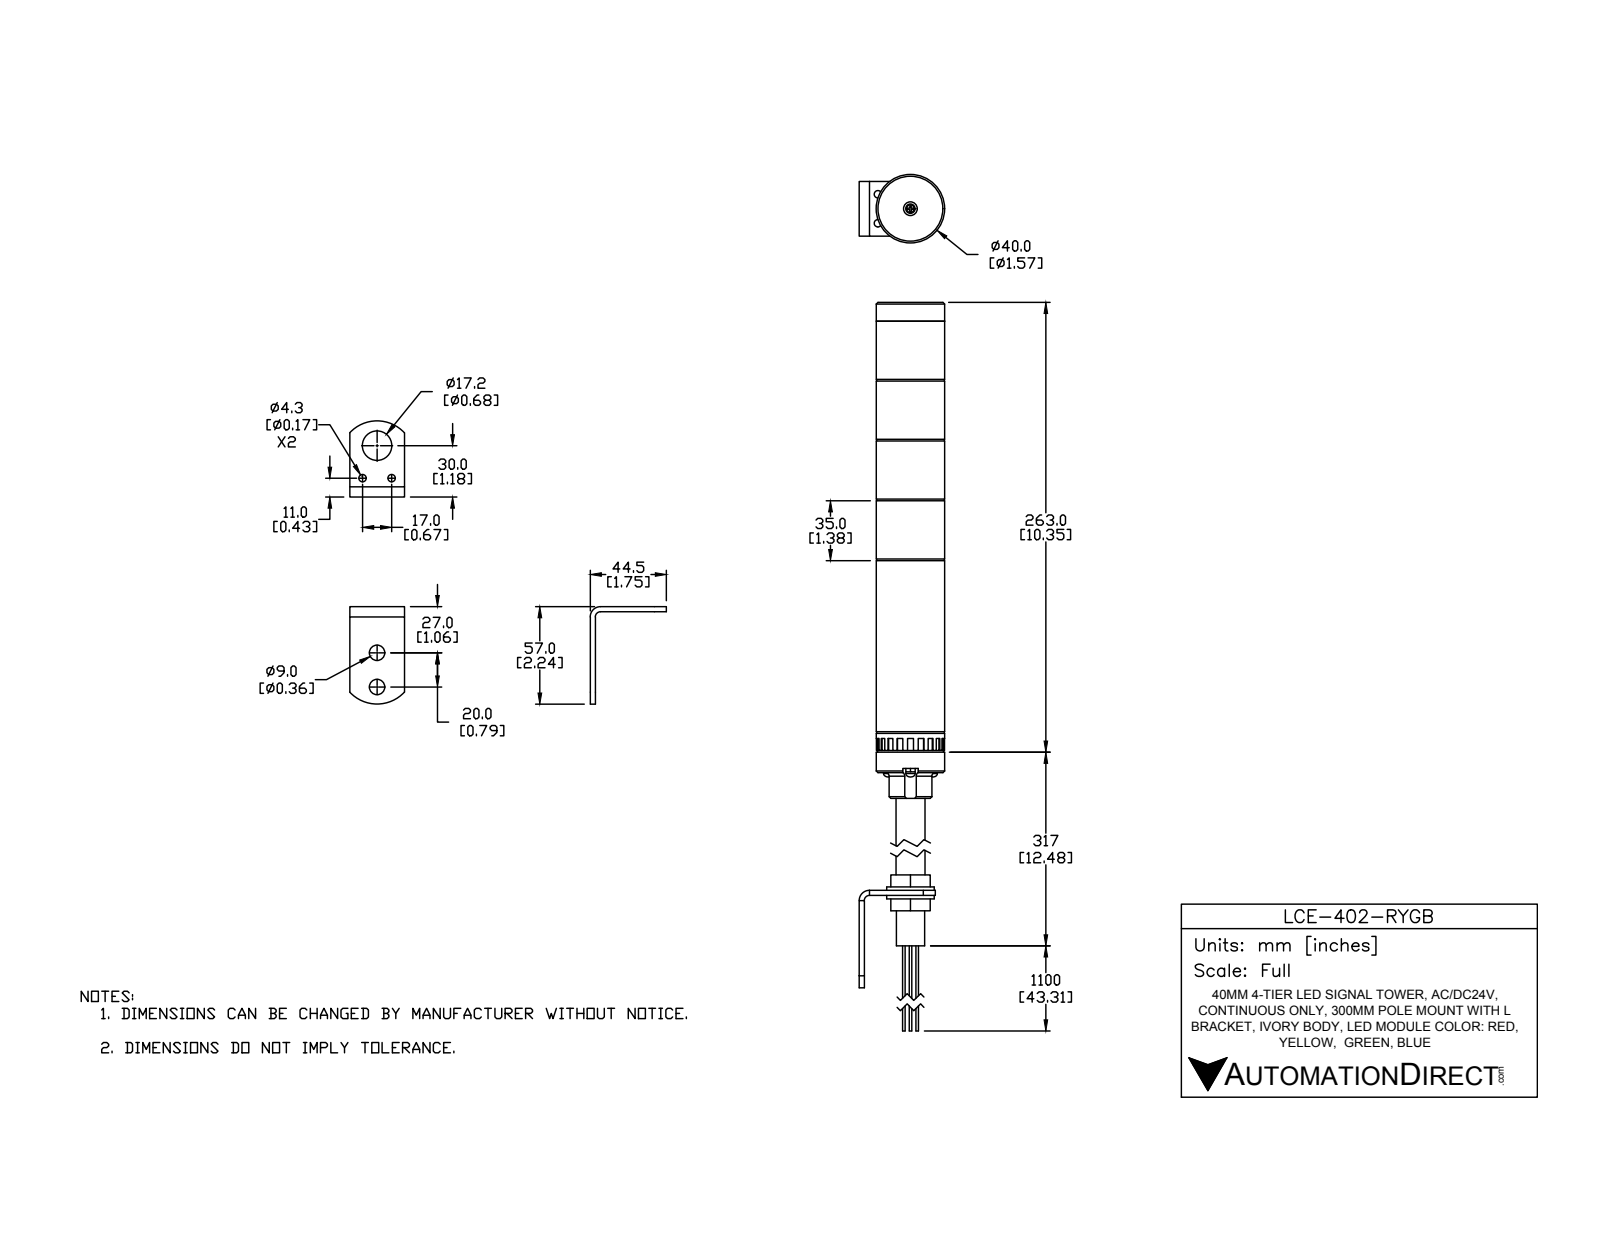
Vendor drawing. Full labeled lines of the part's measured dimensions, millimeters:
Part name (STEP PRODUCT): LCE-402-RYGB
STEP written by: SolidWorks 2016 (AUTOMOTIVE_DESIGN)
Units: millimetres
Bodies: 36 solids, 389 faces (247 planar, 122 cylindrical, 20 other)
Overall size (bounding box): 681 × 50 × 40
Volume: 404 526 mm³ · Surface area: 136 157 mm²
Round holes (diameter × count): ⌀3.5 ×3, ⌀4 ×3, ⌀4.3 ×2, ⌀9.04 ×2, ⌀8 ×1, ⌀12 ×1, ⌀17.2 ×1, ⌀17.5 ×1, ⌀18 ×1
Round bosses / shafts (diameter × count): ⌀3 ×6, ⌀1.5 ×6, ⌀5.5 ×4, ⌀40 ×1, ⌀39.5 ×1, ⌀38.5 ×1, ⌀27.8 ×1, ⌀17 ×1
Partial cylindrical surfaces — rounded edges, fillets, slot ends (radius × count): R4.5 ×3, R21.79 ×2, R3 ×1, R6 ×1, R12.5 ×1
Main face-to-face distances: 35, 1, 70, 34, 36, 105, 69, 11, 71, 104
Hole centre spacings: 15, 25.98, 20.81, 6.09, 17, 17.09, 20, 20.08
